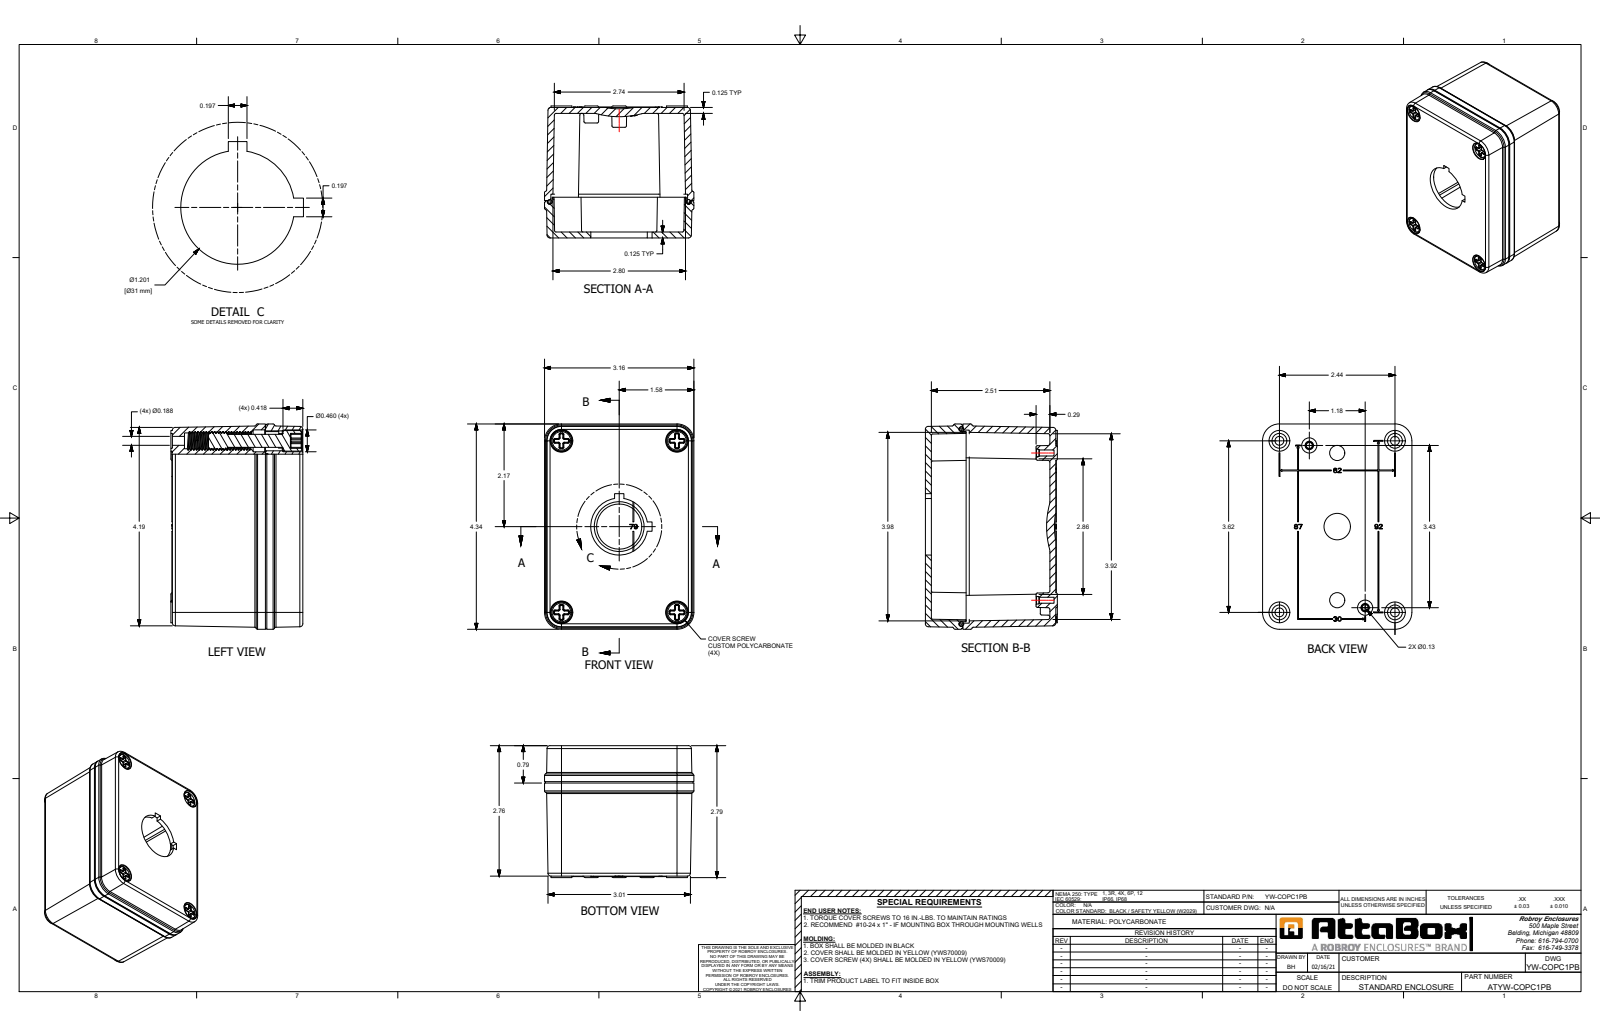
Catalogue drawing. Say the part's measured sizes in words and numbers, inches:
The part is named "YW-COPC1PB". Its 3-D file was written by "SolidWorks 2023 (AUTOMOTIVE_DESIGN)". It is 7 solids with 1146 faces: 266 planar, 426 cylindrical and 454 other. Overall it measures 4.336 by 3.155 by 2.787 inches. Its volume is 10.24 cubic inches and its surface area 152.8 square inches. Round holes: 6 of diameter 0.1, 4 of diameter 0.126, 4 of diameter 0.157, 4 of diameter 0.187, 4 of diameter 0.312, 4 of diameter 0.316, 4 of diameter 0.46, 4 of diameter 0.465, 1 of diameter 1.201. Round bosses or shafts: 4 of diameter 0.44, 4 of diameter 0.433, 4 of diameter 0.276, 2 of diameter 0.1. Partial cylindrical surfaces (rounded edges, fillets, slot ends): 50 of radius 0.02, 48 of radius 0.01, 24 of radius 0.03, 12 of radius 0.015, 12 of radius 0.033, 12 of radius 0.04, 8 of radius 0.063, 8 of radius 0.07. The main face-to-face distances are 0.135, 2.755, 0.125, 2.63, 2.63, 2.505, 0.125, 0.161, 2.779, 2.914. The hole center spacings are 1.247, 2.184, 3.581, 0.57, 0.611, 0.637, 1.555, 1.811.
